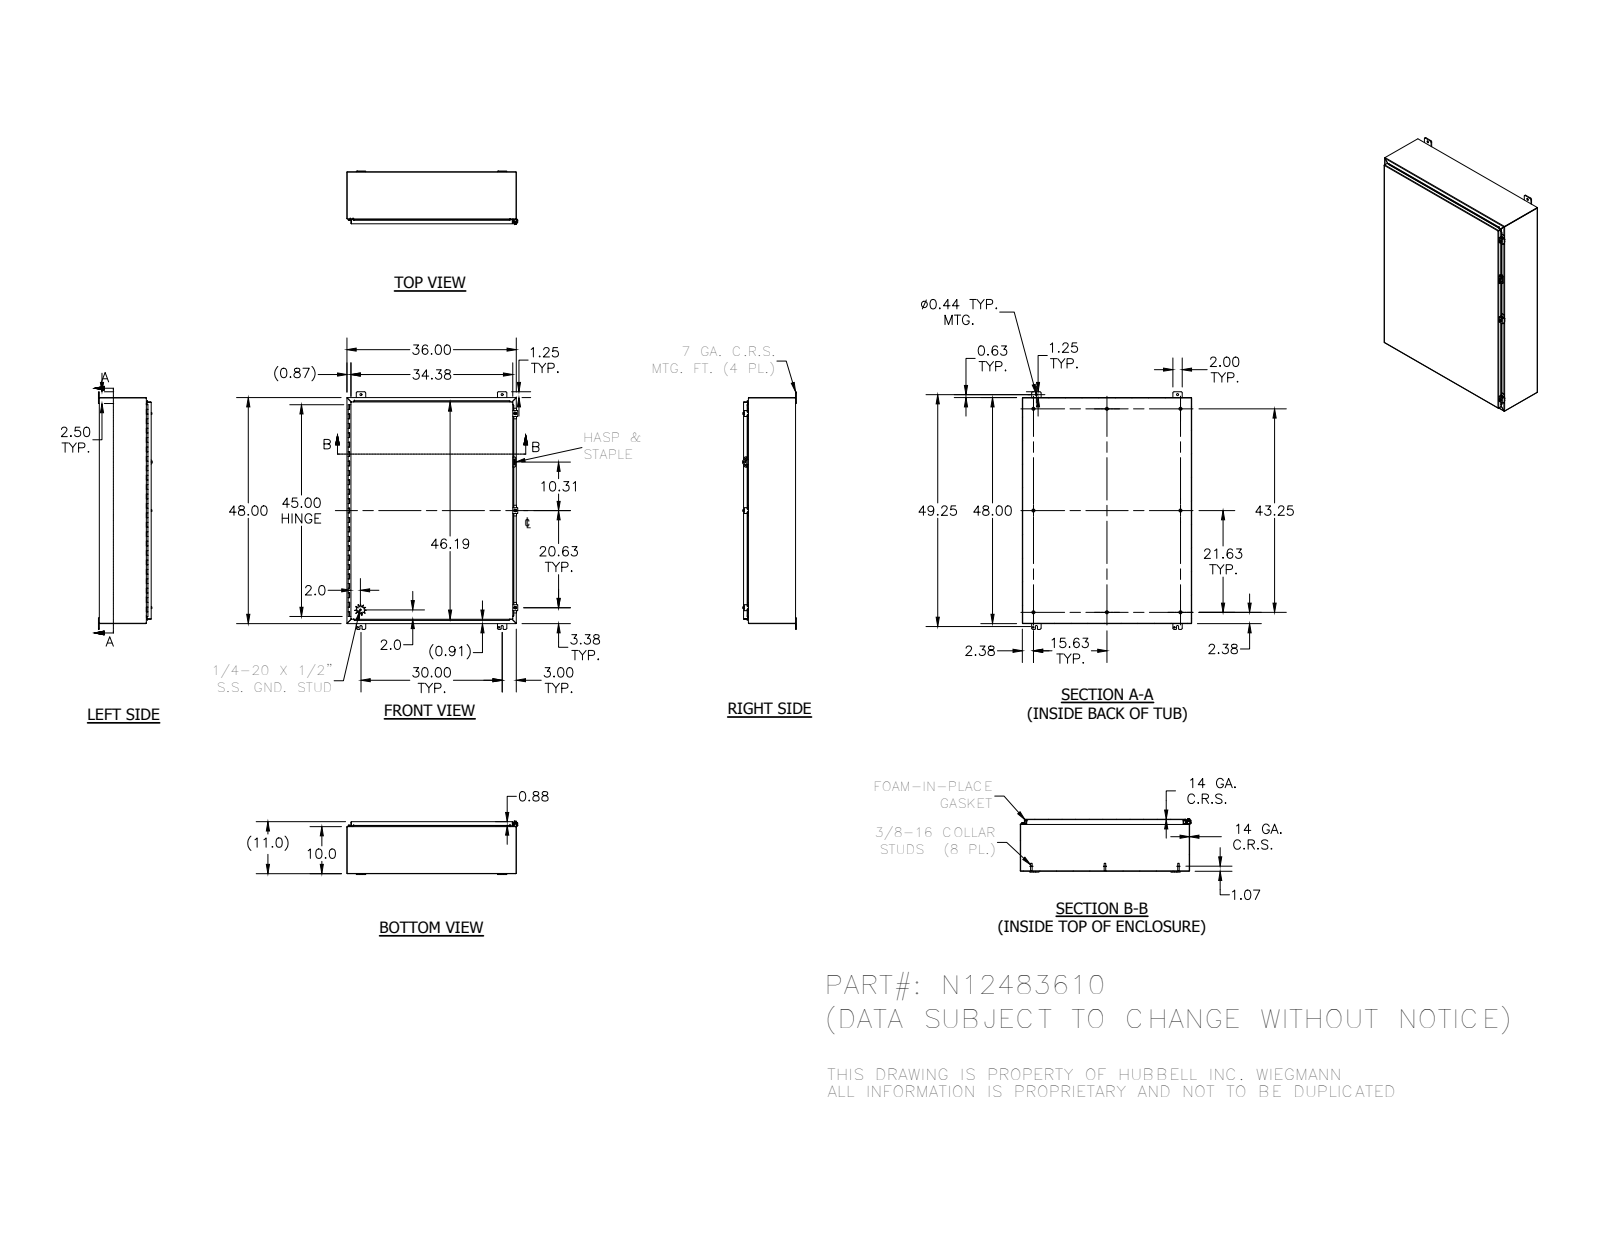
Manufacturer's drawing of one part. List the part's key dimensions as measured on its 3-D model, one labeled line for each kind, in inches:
Part name (STEP PRODUCT): N12483610; 34840; 38413; N123610TB (+8 more)
STEP written by: Autodesk Inventor 2012 (AUTOMOTIVE_DESIGN)
Units: inches
Bodies: 38 solids, 1249 faces (734 planar, 392 cylindrical, 123 other)
Overall size (bounding box): 50.5 × 36.311 × 11.41
Volume: 435.1 in³ · Surface area: 11 520 in²
Round holes (diameter × count): ⌀0.313 ×4, ⌀0.438 ×4, ⌀0.11 ×3, ⌀0.211 ×3, ⌀0.281 ×3, ⌀0.3 ×3, ⌀0.125 ×1, ⌀0.156 ×1, ⌀0.5 ×1
Round bosses / shafts (diameter × count): ⌀0.625 ×8, ⌀0.33 ×8, ⌀0.25 ×5, ⌀0.52 ×3, ⌀0.5 ×3, ⌀0.35 ×3, ⌀0.337 ×1, ⌀0.12 ×1
Partial cylindrical surfaces — rounded edges, fillets, slot ends (radius × count): R0.03 ×39, R0.125 ×27, R0.25 ×27, R0.031 ×21, R0.105 ×21, R0.063 ×15, R0.1 ×6, R0.141 ×6
Main face-to-face distances: 0.074, 10.959, 10.885, 11.033, 35.926, 47.926, 35.852, 36, 9.926, 1.033
Hole centre spacings: 1.593, 30, 48, 56.604, 0.791, 10.327, 29.348, 30.72
